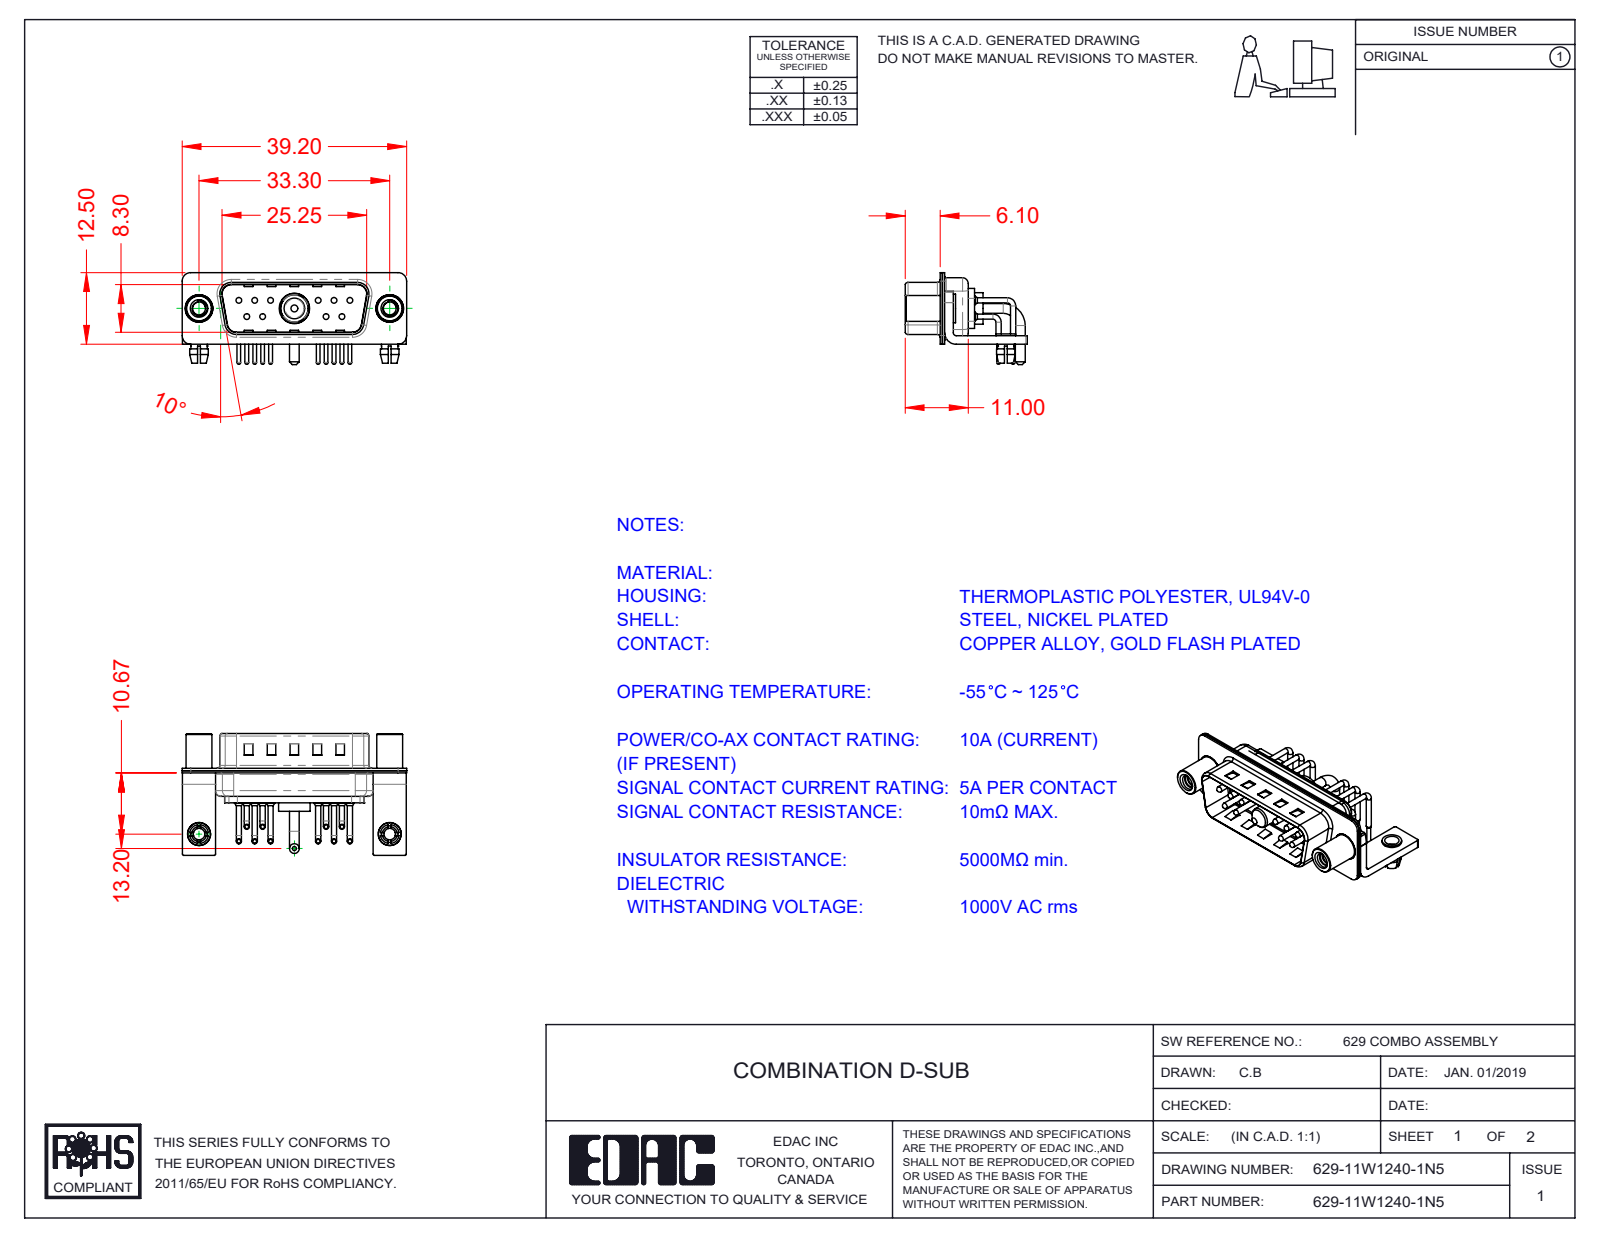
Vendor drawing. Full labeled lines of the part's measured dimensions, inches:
Part name (STEP PRODUCT): 629Combo Threaded Standoff_5; 629Combo Shell Front_15 Contacts; 629Combo Shell Rear_15 Contacts; Power Pin_10A RA (+6 more)
STEP written by: SolidWorks 2020 (CONFIG_CONTROL_DESIGN)
Units: inches
Bodies: 21 solids, 1676 faces (868 planar, 610 cylindrical, 198 other)
Overall size (bounding box): 1.543 × 0.839 × 0.632
Volume: 0.149 in³ · Surface area: 9.777 in²
Round holes (diameter × count): ⌀0.079 ×12, ⌀0.03 ×10, ⌀0.063 ×10, ⌀0.089 ×2, ⌀0.098 ×2, ⌀0.126 ×2, ⌀0.157 ×2, ⌀0.189 ×2, ⌀0.191 ×1, ⌀0.209 ×1
Round bosses / shafts (diameter × count): ⌀0.035 ×20, ⌀0.059 ×10, ⌀0.039 ×10, ⌀0.026 ×10, ⌀0.197 ×2, ⌀0.193 ×2, ⌀0.177 ×2, ⌀0.157 ×2
Partial cylindrical surfaces — rounded edges, fillets, slot ends (radius × count): R0.01 ×16, R0.059 ×16, R0.079 ×13, R0.04 ×10, R0.02 ×9, R0.063 ×8, R0.039 ×7, R0.024 ×4
Main face-to-face distances: 0.016, 0.031, 0.059, 0.374, 0.358, 0.343, 0.39, 0.024, 0.075, 0.205
Hole centre spacings: 0.124, 0.109, 0.545, 0.436, 0.654, 0.198, 0.198, 0.218
